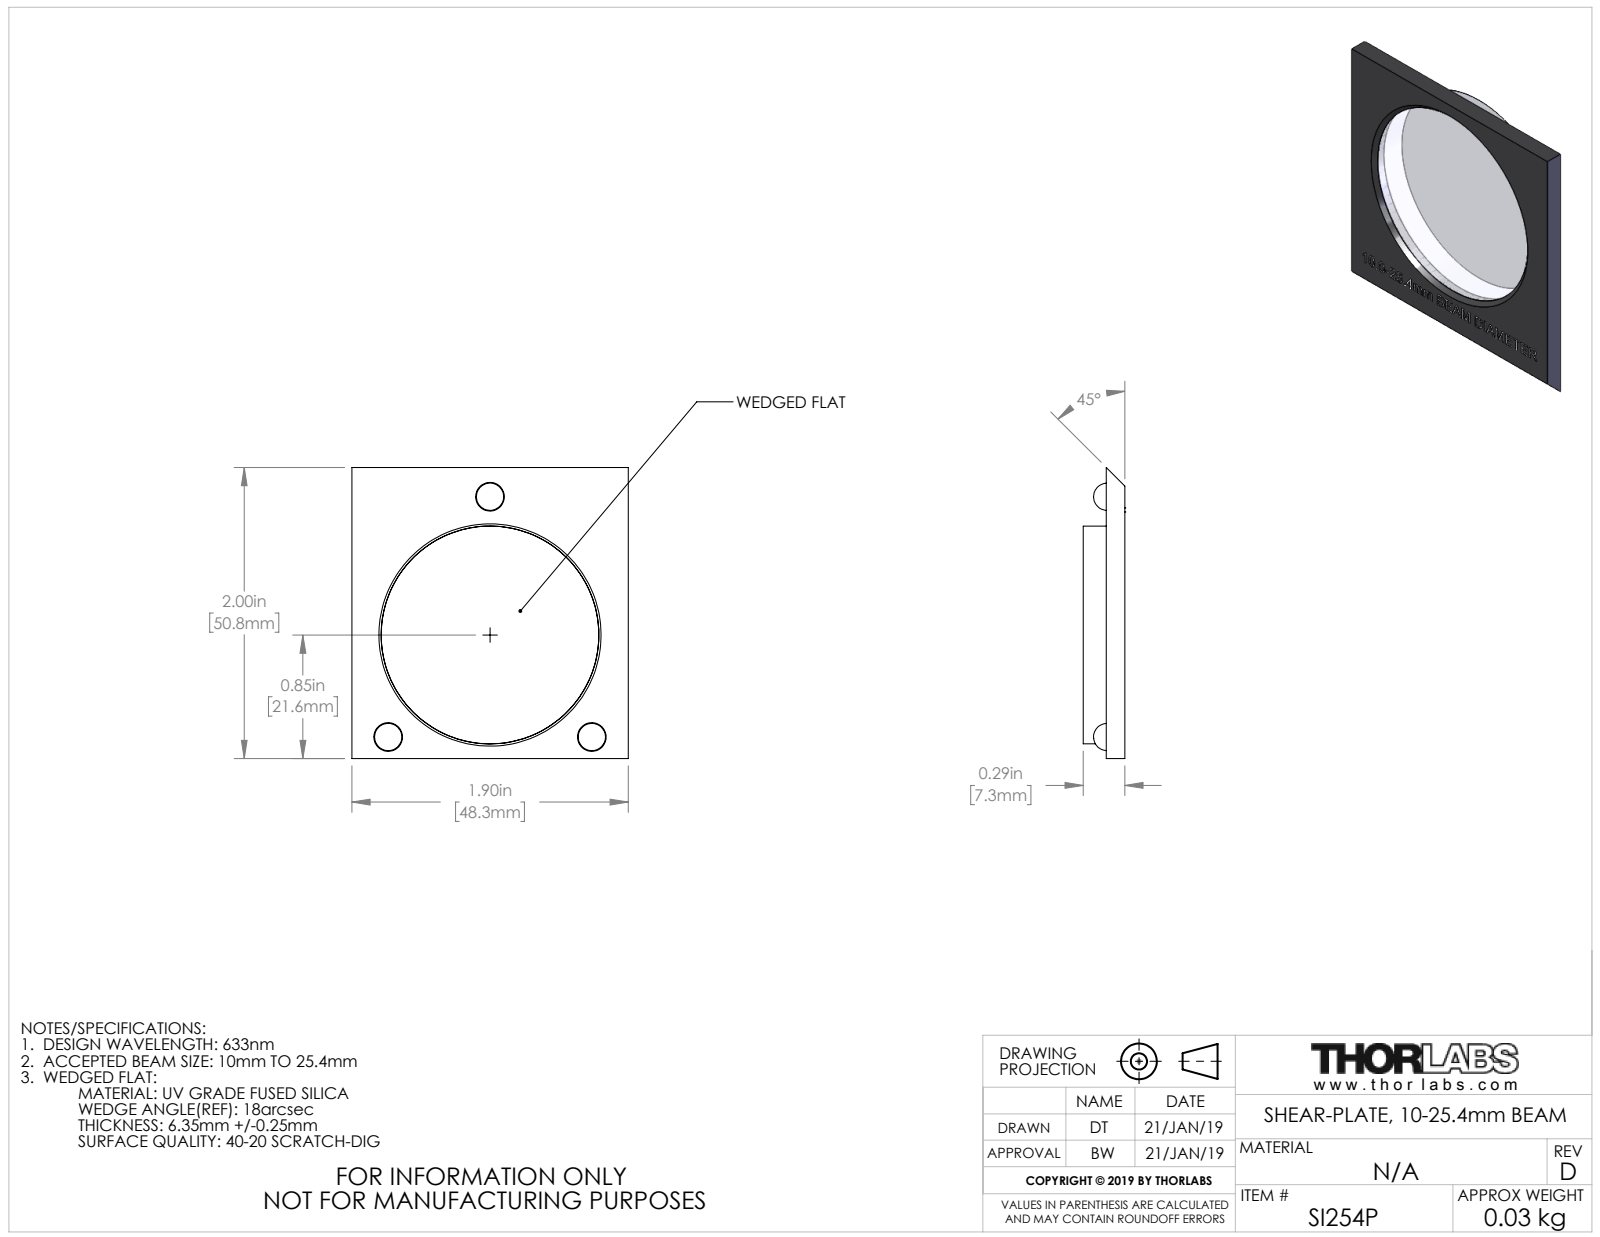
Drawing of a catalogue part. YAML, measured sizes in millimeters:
part_name: "16657-E0W"
step_written_by: "SolidWorks 2018 (CONFIG_CONTROL_DESIGN)"
units: millimeters
bodies: {solids: 5, faces: 350, planar: 230, cylindrical: 12, other: 108}
overall_size: [50.8, 48.3, 7.3]
volume: 11200
surface_area: 6942
round_holes:
  - {diameter: 4.7, count: 3}
  - {diameter: 37, count: 1}
  - {diameter: 38, count: 1}
round_bosses_or_shafts:
  - {diameter: 38, count: 1}
face_to_face_distances: [2.3, 6.3, 4, 1, 3.3, 7.3, 48.3, 2.5, 6.6, 0.7]
hole_center_spacings: [25.2, 45.5, 24.1, 35.6]
